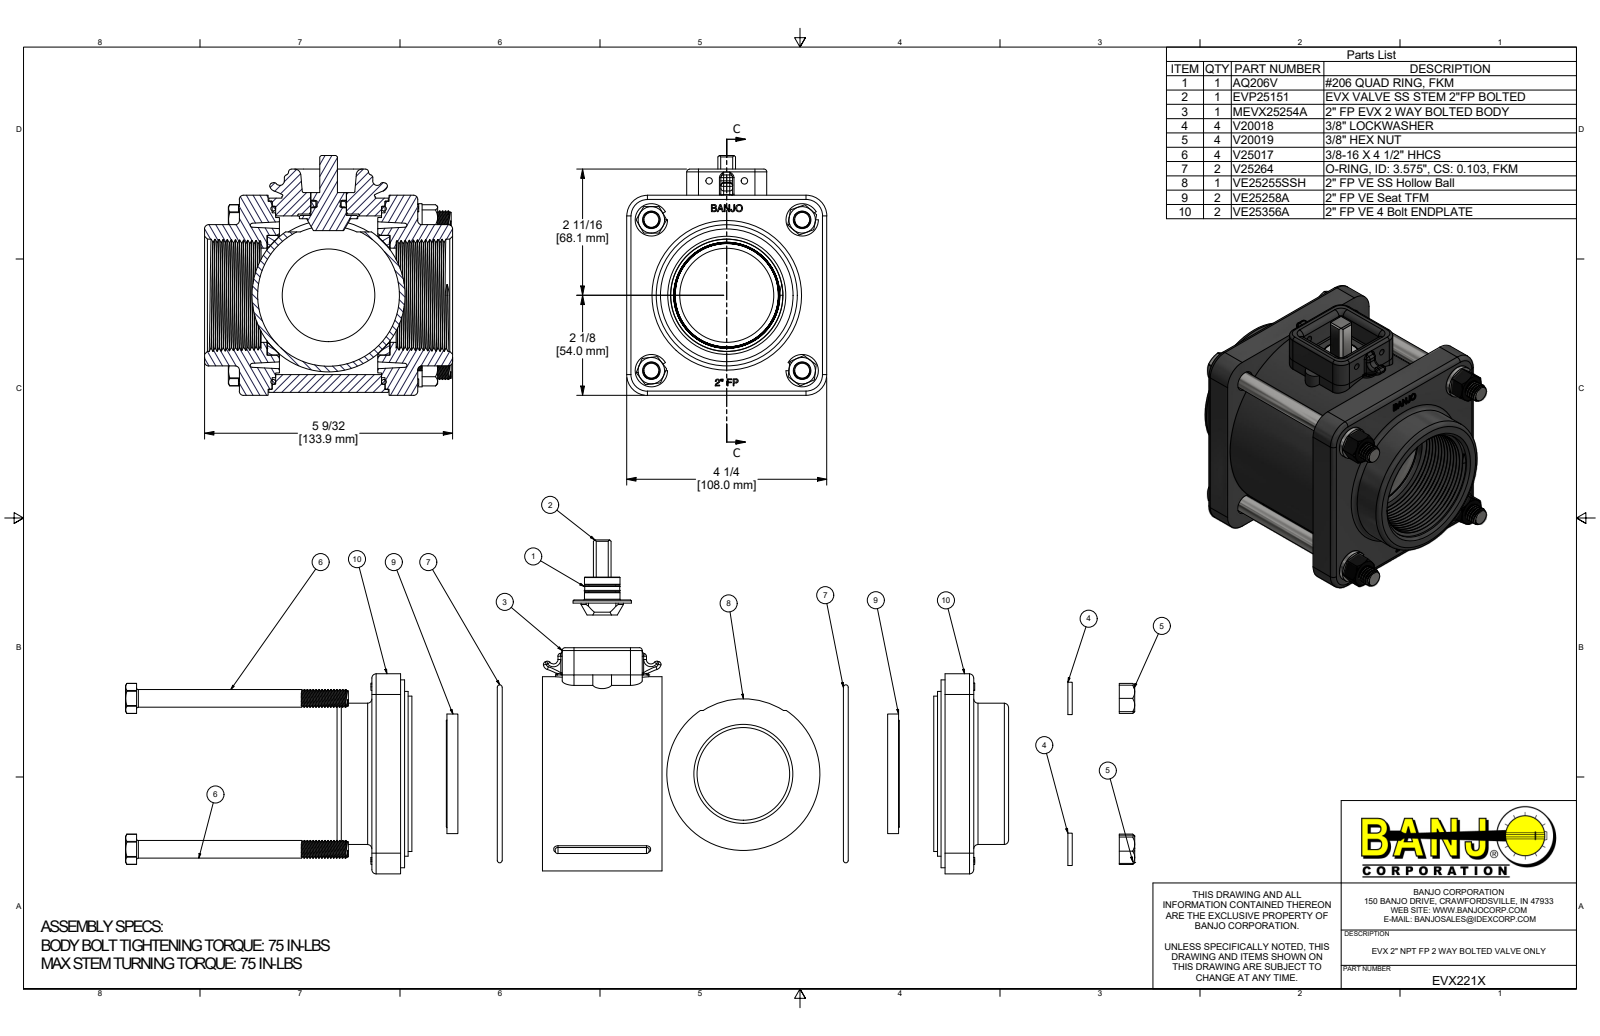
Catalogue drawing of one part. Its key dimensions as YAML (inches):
part_name: "EVX221X; MEVX25254A; MEVX25254AX; V25017 (+8 more)"
step_written_by: "Autodesk Inventor 2019 (AUTOMOTIVE_DESIGN)"
units: inches
bodies: {solids: 22, faces: 1319, planar: 388, cylindrical: 386, other: 545}
overall_size: [5.27, 5.093, 4.25]
volume: 39.67
surface_area: 342.8
round_holes:
  - {diameter: 0.307, count: 4}
  - {diameter: 0.385, count: 4}
  - {diameter: 0.438, count: 4}
  - {diameter: 0.135, count: 2}
  - {diameter: 0.76, count: 1}
  - {diameter: 1.3, count: 1}
  - {diameter: 1.97, count: 1}
  - {diameter: 2, count: 1}
  - {diameter: 2.045, count: 1}
  - {diameter: 2.545, count: 1}
  - {diameter: 3.37, count: 1}
  - {diameter: 3.78, count: 1}
round_bosses_or_shafts:
  - {diameter: 0.324, count: 60}
  - {diameter: 0.687, count: 4}
  - {diameter: 0.375, count: 4}
  - {diameter: 4.125, count: 1}
  - {diameter: 3.99, count: 1}
  - {diameter: 3.5, count: 1}
  - {diameter: 3.3, count: 1}
  - {diameter: 3, count: 1}
partial_cylinders:
  - {radius: 0.06, count: 24}
  - {radius: 0.03, count: 12}
  - {radius: 0.09, count: 10}
  - {radius: 0.062, count: 8}
  - {radius: 0.162, count: 8}
  - {radius: 0.125, count: 6}
  - {radius: 0.02, count: 4}
  - {radius: 0.21, count: 4}
face_to_face_distances: [0.61, 3.18, 3.79, 0.695, 3.095, 0.085, 2.485, 4.25, 0.16, 0.77]
hole_center_spacings: [2.265, 3.204, 1.48, 2.143, 2.458, 4.214, 4.49, 4.531]
